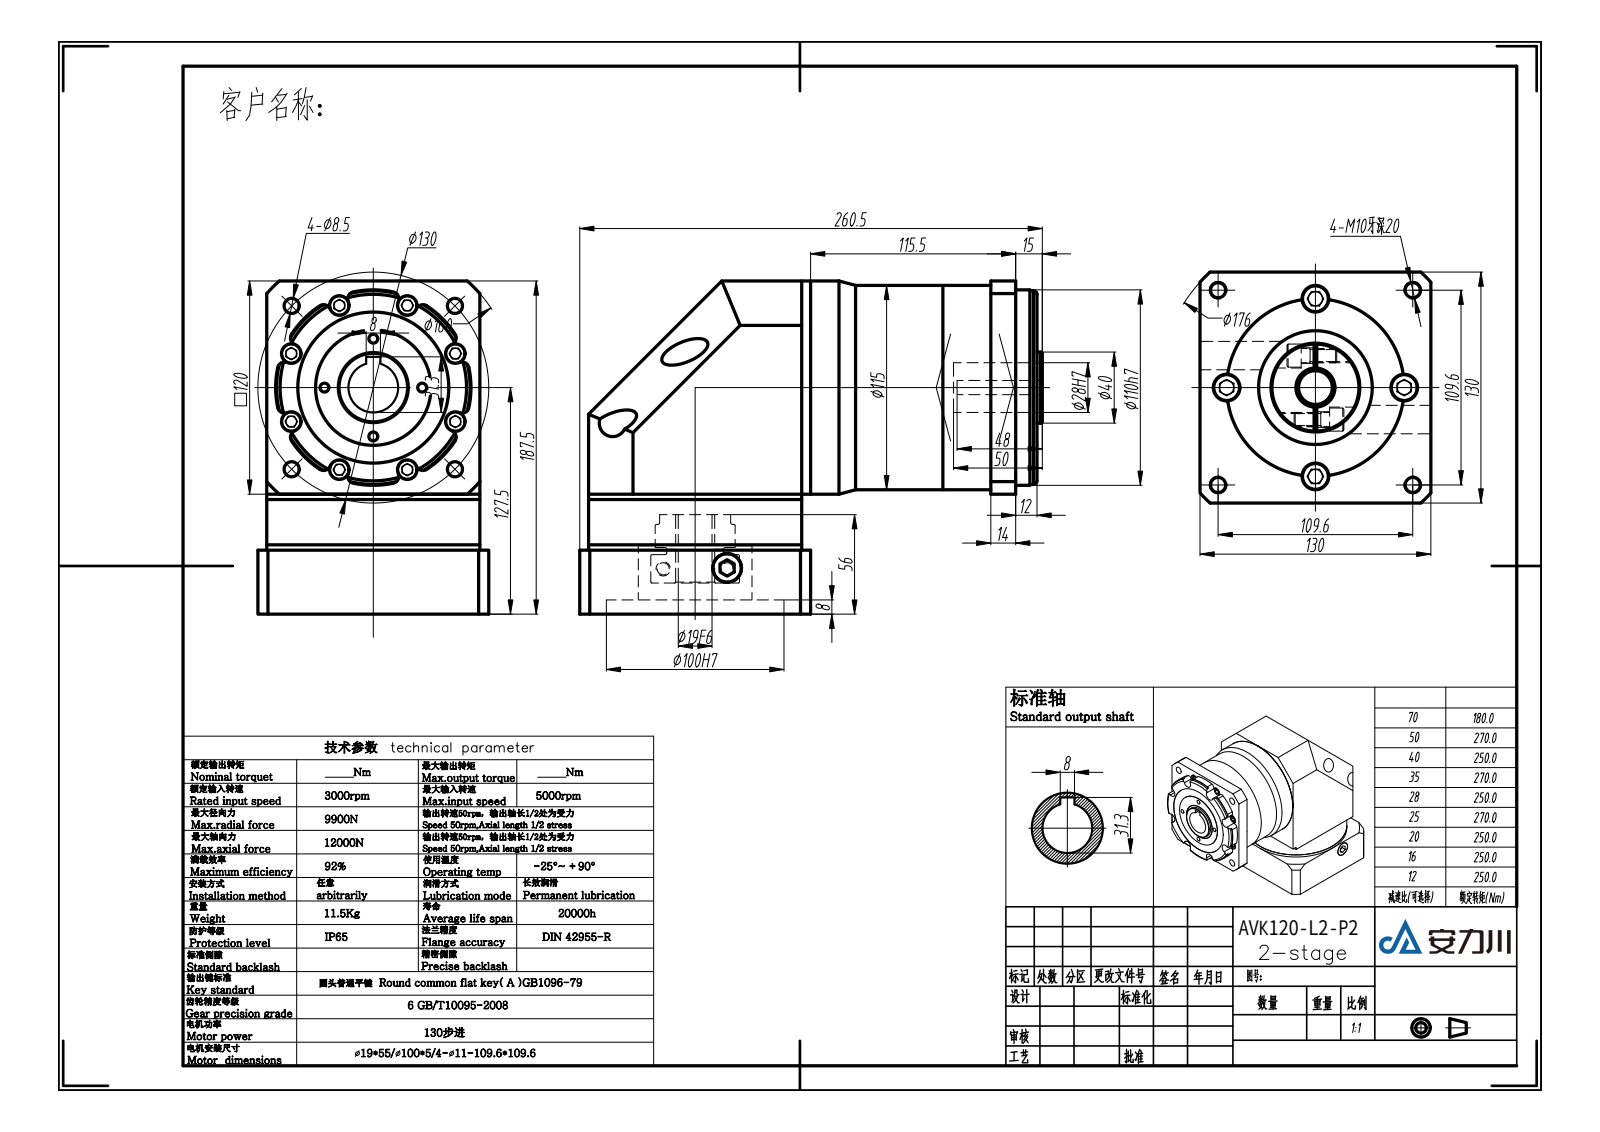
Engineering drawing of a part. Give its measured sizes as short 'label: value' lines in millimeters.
name: VGZK115双级模型（19-55 100-5 4-11-109.6-109.6）
written by: SolidWorks 2016 (AUTOMOTIVE_DESIGN)
unit: mm
bodies: 23 solids, 503 faces (276 planar, 202 cylindrical, 25 other)
size: 260.5 × 187.5 × 130
volume: 3 422 000 mm³; area: 357 293 mm²
holes: 10× ⌀15, 8× ⌀8.5, 8× ⌀11, 4× ⌀5, 2× ⌀16, 1× ⌀19, 1× ⌀20, 1× ⌀22, 1× ⌀28, 1× ⌀45.2, 1× ⌀70, 1× ⌀85
bosses: 10× ⌀13, 8× ⌀9.5, 2× ⌀120, 2× ⌀15.6, 1× ⌀115, 1× ⌀65, 1× ⌀50, 1× ⌀45
rounds: 16× R4, 1× R54.5, 1× R55, 1× R80, 1× R88
face distances: 5, 25.5, 49.17, 74.5, 79.5, 25.33, 30.33, 120, 125, 3
hole spacings: 39.29, 94.69, 26.74, 26.83, 46.94, 49.53, 49.99, 55.01
